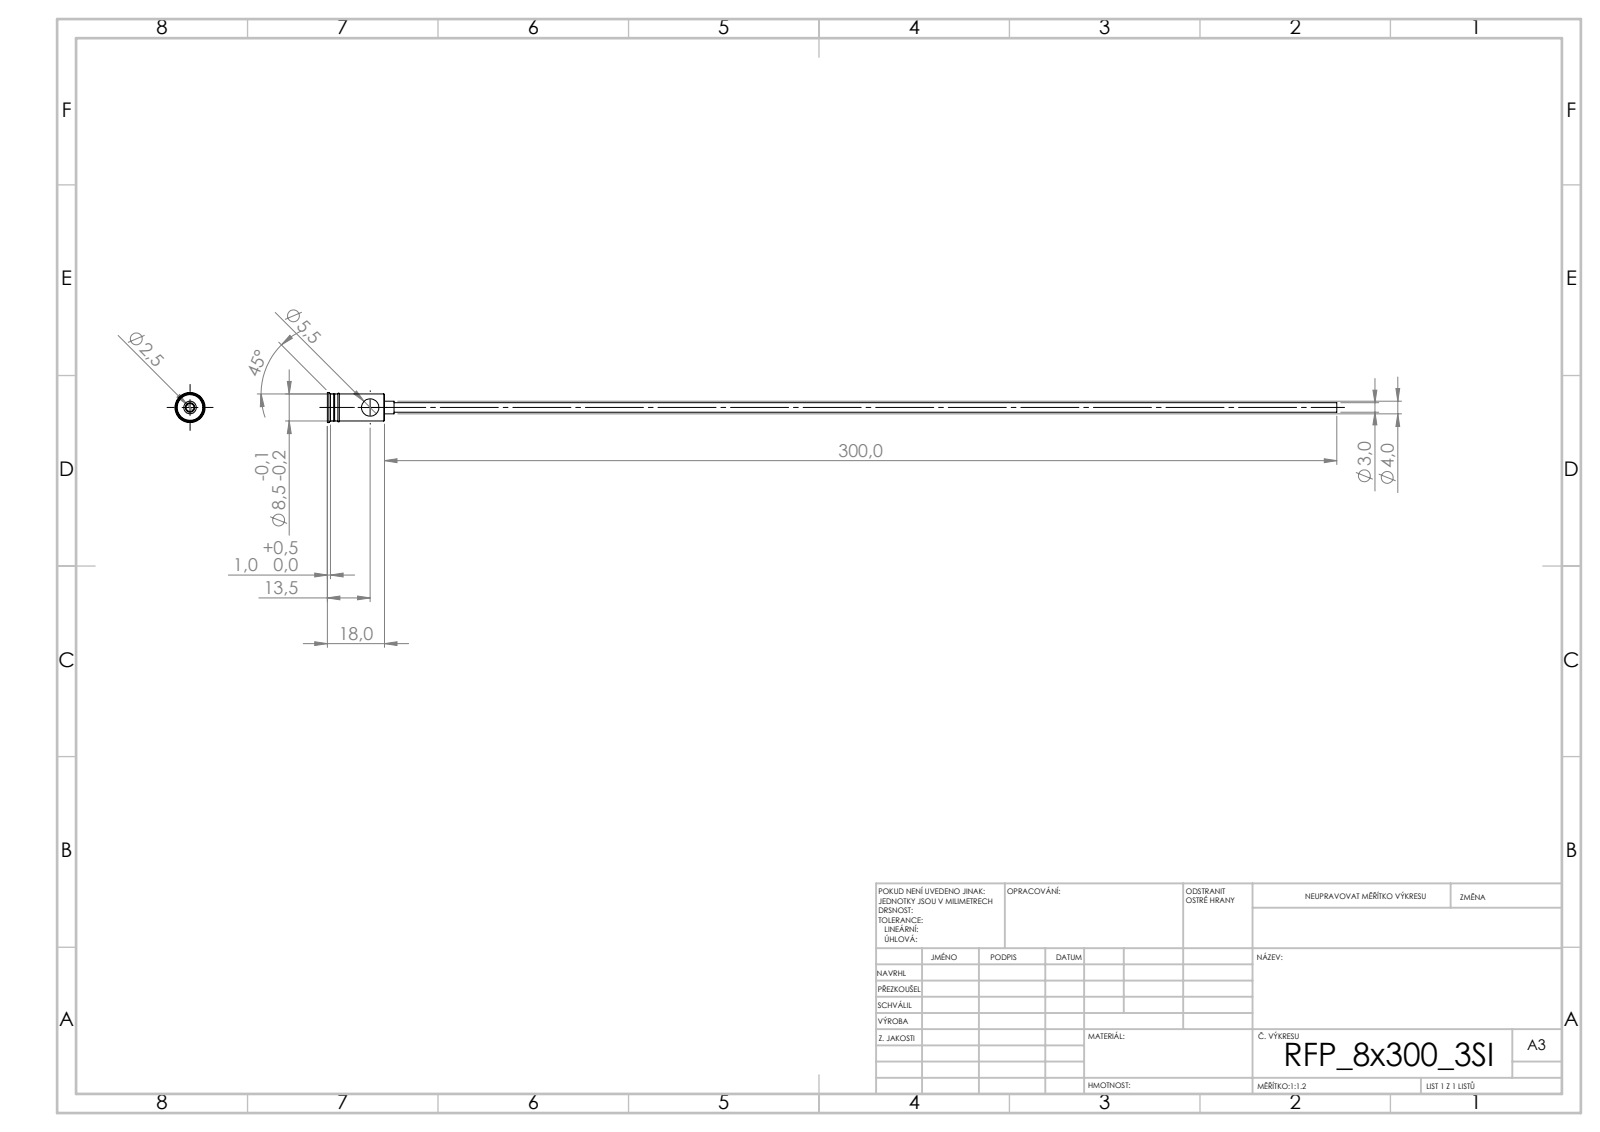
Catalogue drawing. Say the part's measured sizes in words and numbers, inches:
Its 3-D file was written by "SolidWorks 2019 (CONFIG_CONTROL_DESIGN)". It is 1 solid with 44 faces: 20 planar, 16 cylindrical and 8 other. Overall it measures 12.52 by 0.374 by 0.374 inches. Its volume is 0.09 cubic inches and its surface area 9.204 square inches. Round holes: 1 of diameter 0.098, 1 of diameter 0.217. Round bosses or shafts: 1 of diameter 0.374, 1 of diameter 0.335, 1 of diameter 0.157, 1 of diameter 0.118. The main face-to-face distances are 0.709, 0.63, 0.079, 0.154, 0.618, 0.091, 0.118, 0.736, 0.748, 0.827.
